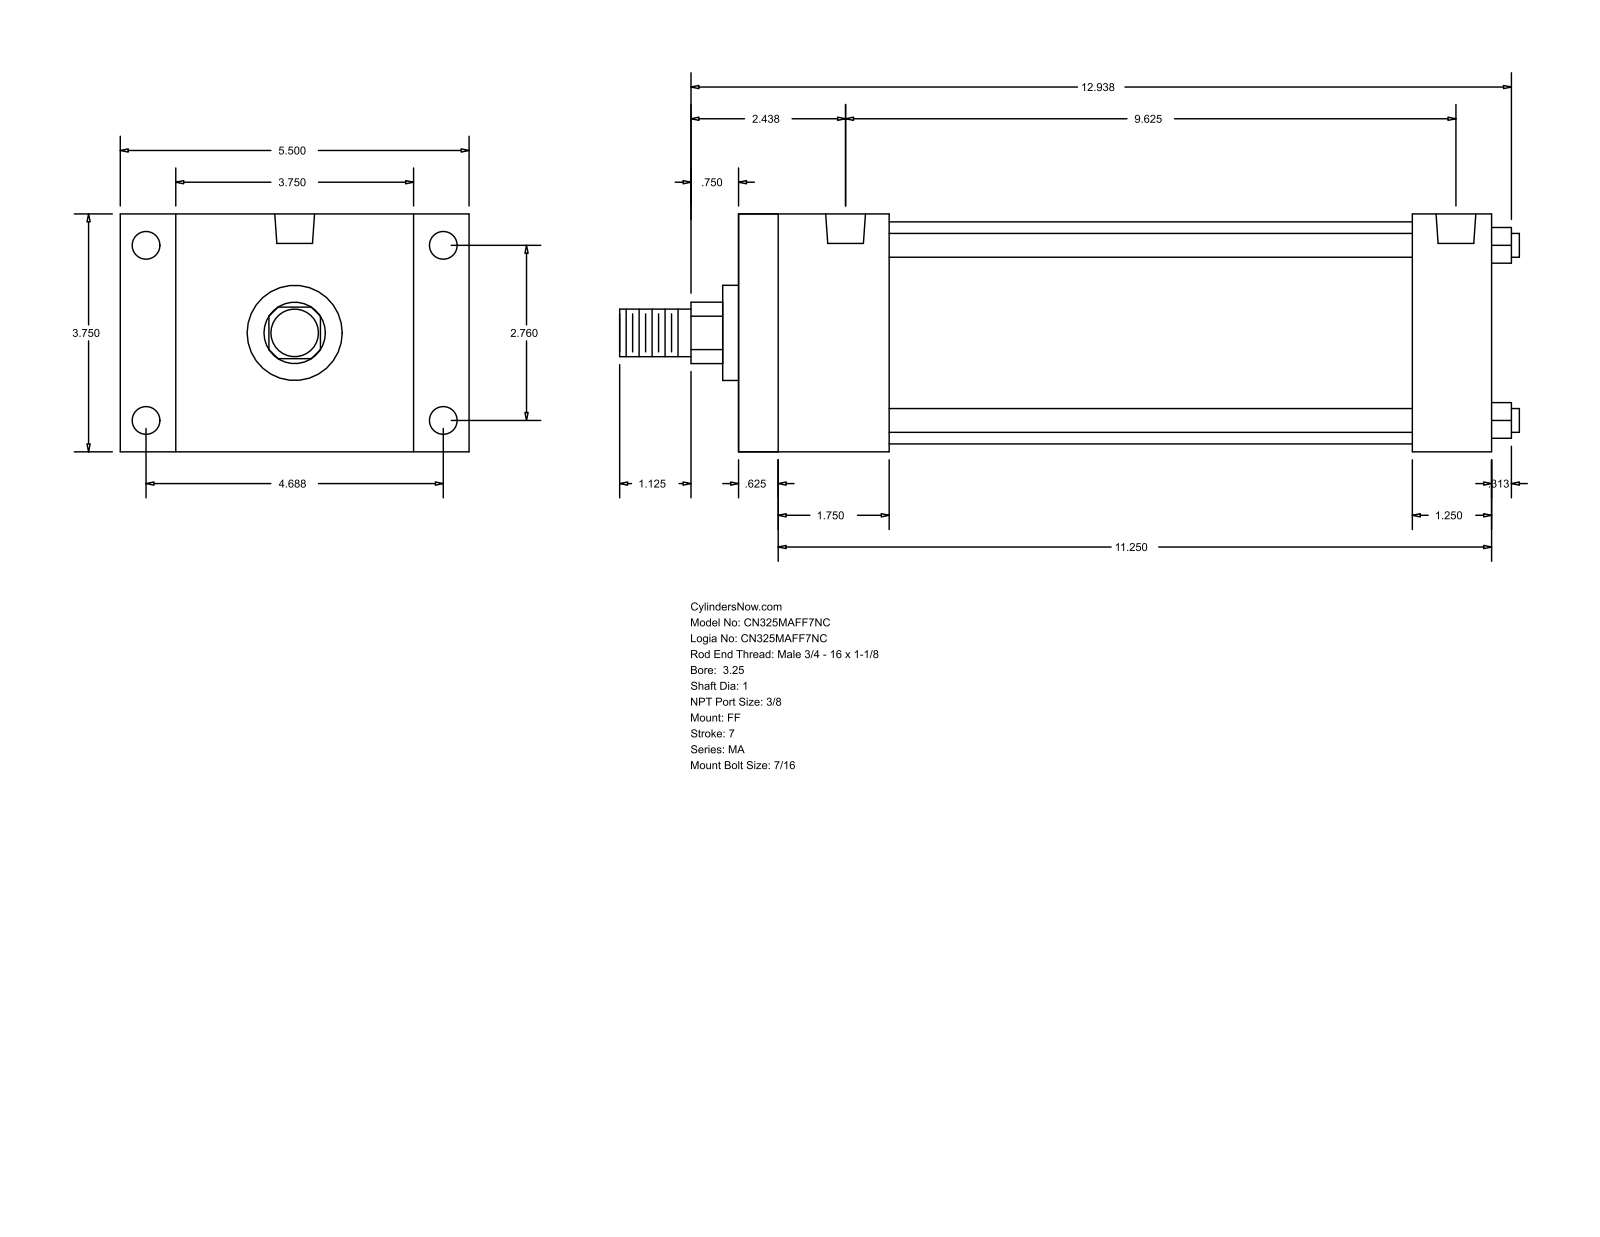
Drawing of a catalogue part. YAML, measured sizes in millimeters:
part_name: "MA_FF__0325_1"
step_written_by: "GSSL Pune (CONFIG_CONTROL_DESIGN)"
units: millimeters
bodies: {solids: 0, faces: 92, planar: 64, cylindrical: 28, other: 0}
overall_size: [360.36, 139.7, 95.25]
round_holes:
  - {diameter: 11.11, count: 8}
  - {diameter: 15.93, count: 2}
round_bosses_or_shafts:
  - {diameter: 9.53, count: 4}
  - {diameter: 88.9, count: 1}
  - {diameter: 38.1, count: 1}
  - {diameter: 25.4, count: 1}
  - {diameter: 19.05, count: 1}
partial_cylinders:
  - {radius: 12.29, count: 1}
face_to_face_distances: [95.24, 301.63, 15.87, 285.76, 22.23, 117.47, 60.33, 269.88, 44.46, 254.01]
hole_center_spacings: [70.1, 119.06, 138.16, 234.95, 4.76, 4.77, 239.71, 239.72]
